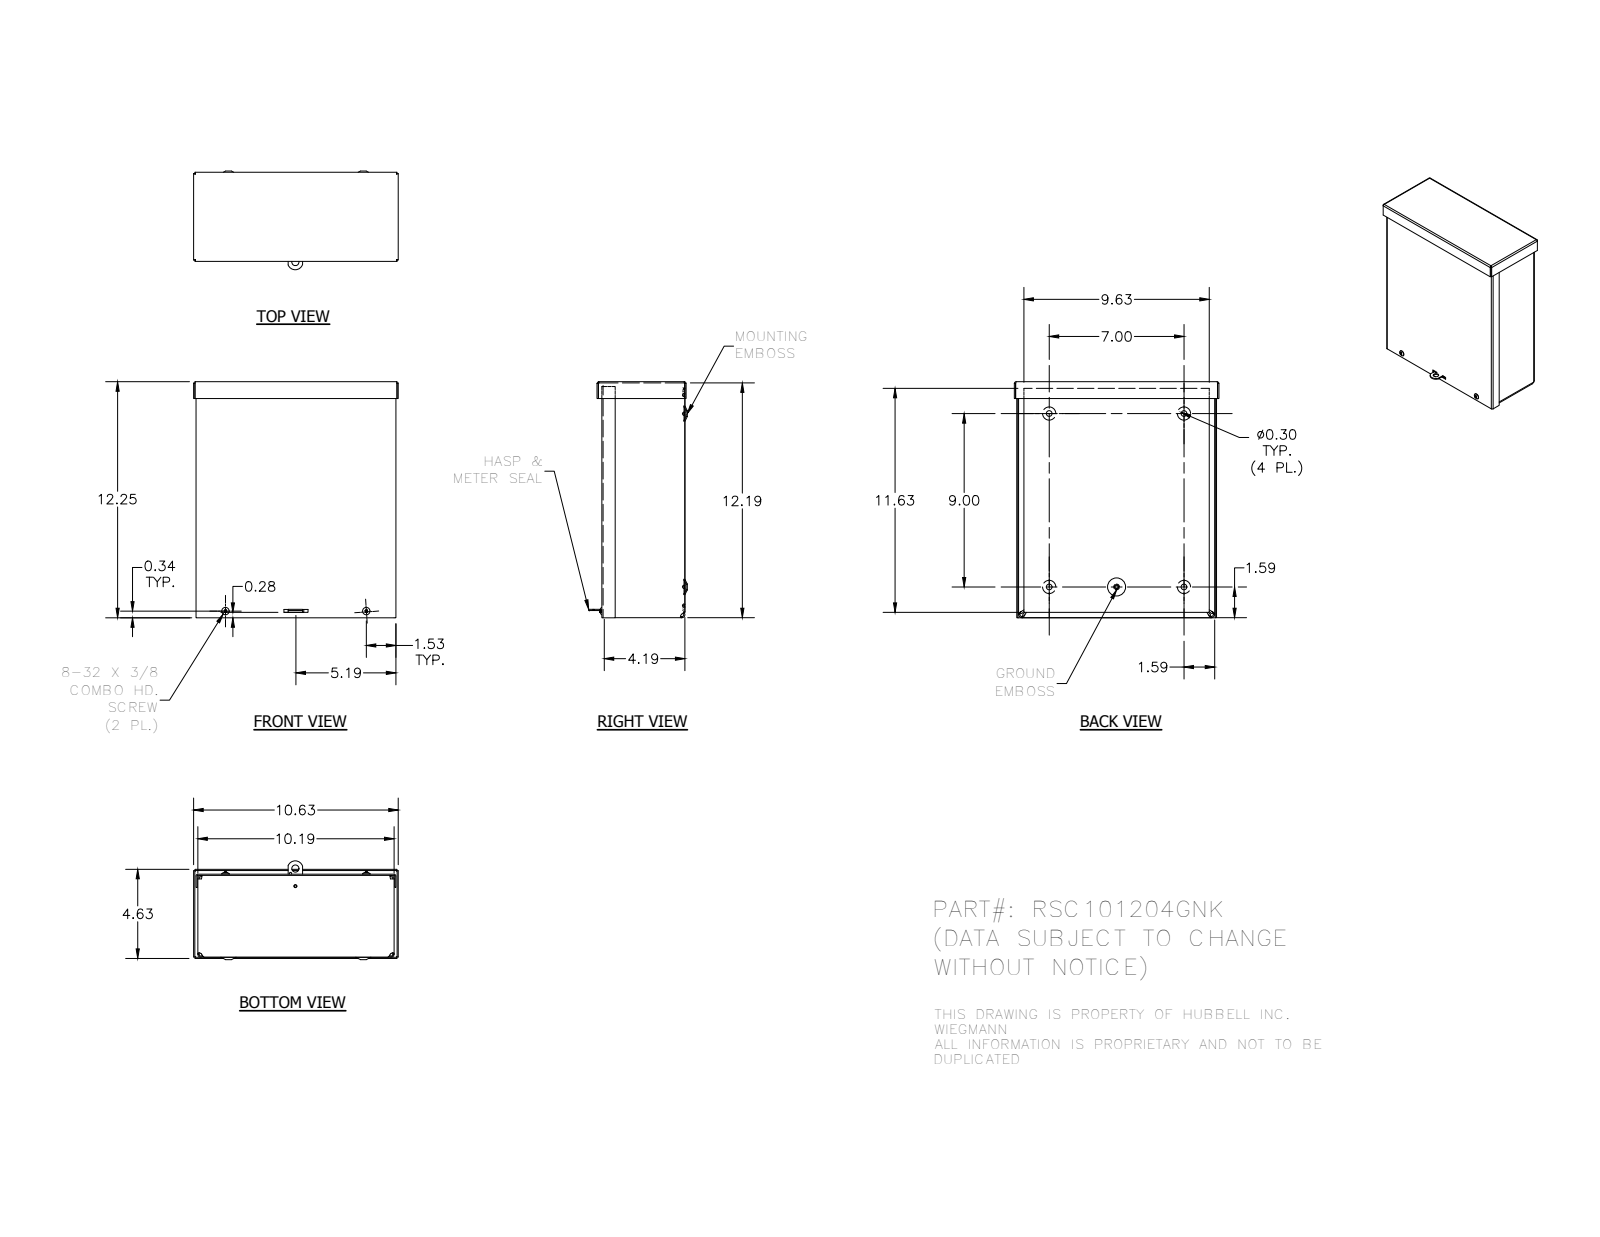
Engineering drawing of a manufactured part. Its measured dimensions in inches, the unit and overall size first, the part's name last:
Units: inches
Overall size (bounding box): 24.406 × 24.25 × 7.125
Round holes (diameter × count): ⌀0.3 ×4, ⌀0.313 ×4, ⌀0.148 ×3, ⌀0.125 ×2, ⌀0.156 ×1, ⌀0.165 ×1, ⌀0.375 ×1
Round bosses / shafts (diameter × count): ⌀0.384 ×2, ⌀0.164 ×2, ⌀0.228 ×1
Partial cylindrical surfaces — rounded edges, fillets, slot ends (radius × count): R0.031 ×8, R0.093 ×8, R0.125 ×8, R0.187 ×8, R0.055 ×4, R0.062 ×4, R0.094 ×4, R0.117 ×4
Main face-to-face distances: 24.126, 0.062, 0.062, 24.188, 6.187, 24.063, 24.187, 24.064, 6.249, 0.063
Hole centre spacings: 3.5, 7, 7.313, 9, 9.656, 11.312, 11.402, 13.47
Volume: 65.72 in³ · Surface area: 2 141 in²
Bodies: 7 solids, 378 faces (163 planar, 79 cylindrical, 136 other)
Part name (STEP PRODUCT): RSC242406GNK_WRAP; RSC1012GNK_LID; RSC1004GNK_CAP; 3183 (+3 more)
STEP written by: Autodesk Inventor 2014 (AUTOMOTIVE_DESIGN)
